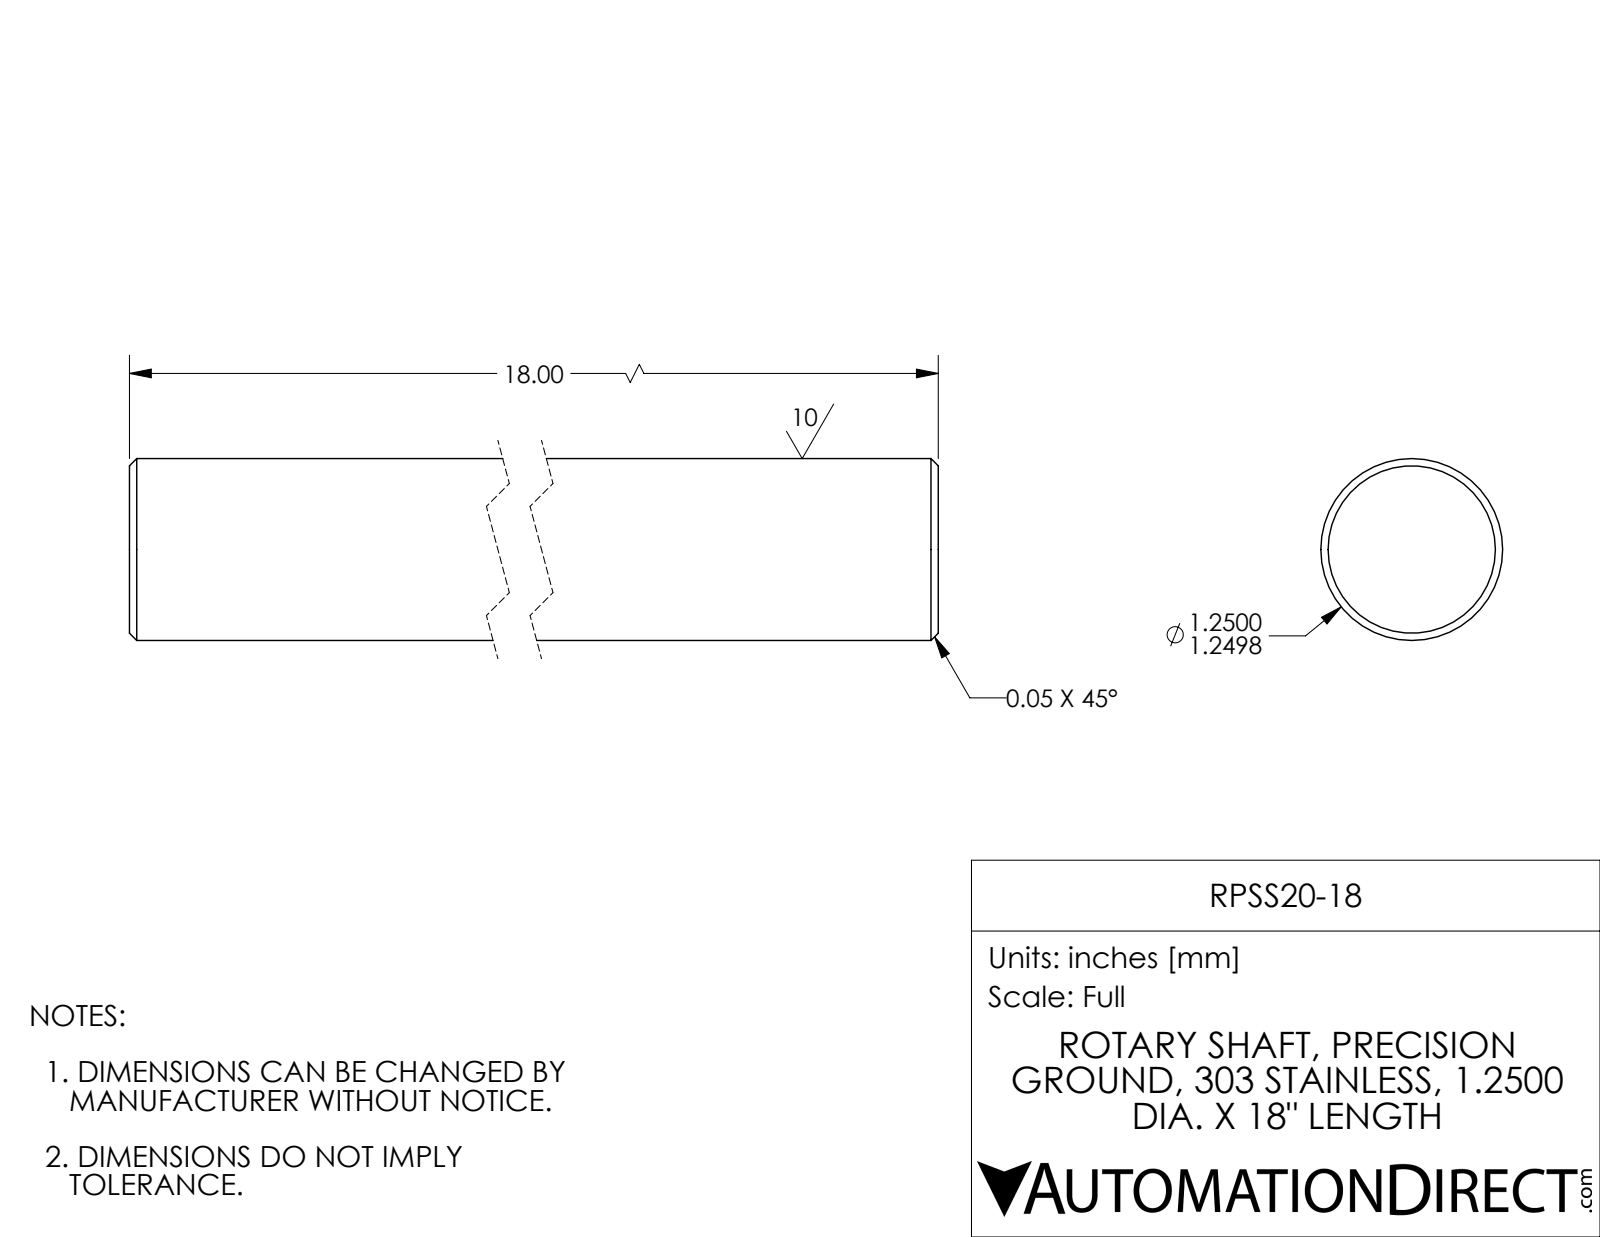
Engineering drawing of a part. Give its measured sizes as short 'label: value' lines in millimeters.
name: RPSS20-18
written by: SolidWorks 2017 (AUTOMOTIVE_DESIGN)
unit: mm
bodies: 1 solid, 8 faces (2 planar, 2 cylindrical, 4 other)
size: 457.2 × 31.8 × 31.8
volume: 361 800 mm³; area: 47 030 mm²
bosses: 1× ⌀31.8
face distances: 457.2
